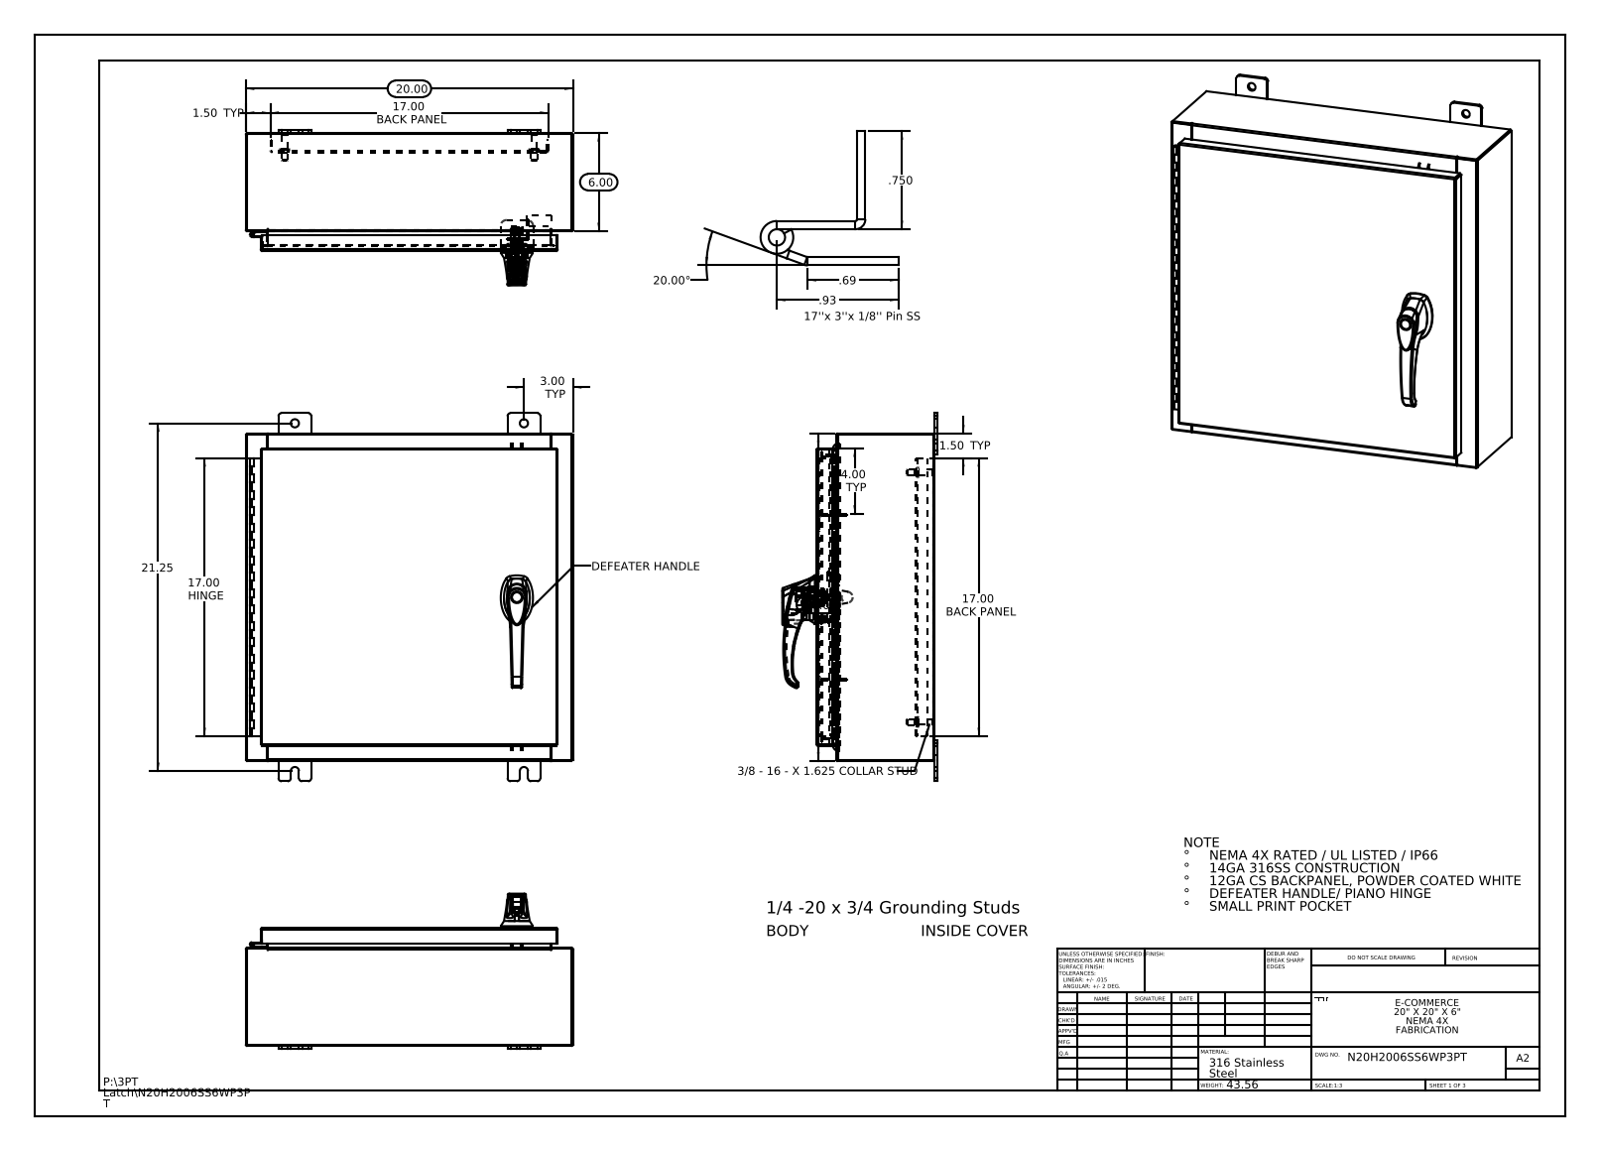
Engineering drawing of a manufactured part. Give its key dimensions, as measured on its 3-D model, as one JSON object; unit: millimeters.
{"part_name": "N20H2006SS6WP3PT Hinge Enclosure Side2; N20H2006SS6WP3PT Defeater Handle - 3 - 2500-51 ZN; N20H2006SS6WP3PT Backpanel; NMP-SS-RODGUIDES (+8 more)", "step_written_by": "SolidWorks 2013 (CONFIG_CONTROL_DESIGN)", "units": "millimeters", "bodies": {"solids": 31, "faces": 2316, "planar": 817, "cylindrical": 845, "other": 654}, "overall_size": [571.5, 508, 241.2], "volume_mm3": 2551000, "surface_area_mm2": 2464000, "round_holes": [[12.7, 8], [6.4, 4], [3.5, 3], [4.1, 3], [2, 2], [5.2, 2], [8, 2], [11.1, 2], [3.2, 1], [3.2, 1], [5, 1], [7, 1]], "round_bosses_or_shafts": [[15.9, 4], [9.5, 4], [8.4, 4], [30, 1], [19, 1], [17.3, 1], [16.8, 1], [16.2, 1]], "partial_cylinders_radius": [[3, 37], [0.2, 33], [4.8, 24], [0.3, 22], [2.2, 18], [1, 15], [0.7, 12], [0.2, 6]], "face_to_face_distances": [1.9, 181, 506.1, 179.1, 182.9, 2.6, 25.4, 27.3, 153.7, 155.6], "hole_center_spacings": [86.5, 7.5, 15.9, 21.4, 31.8, 33.4, 39.6, 47.2]}
